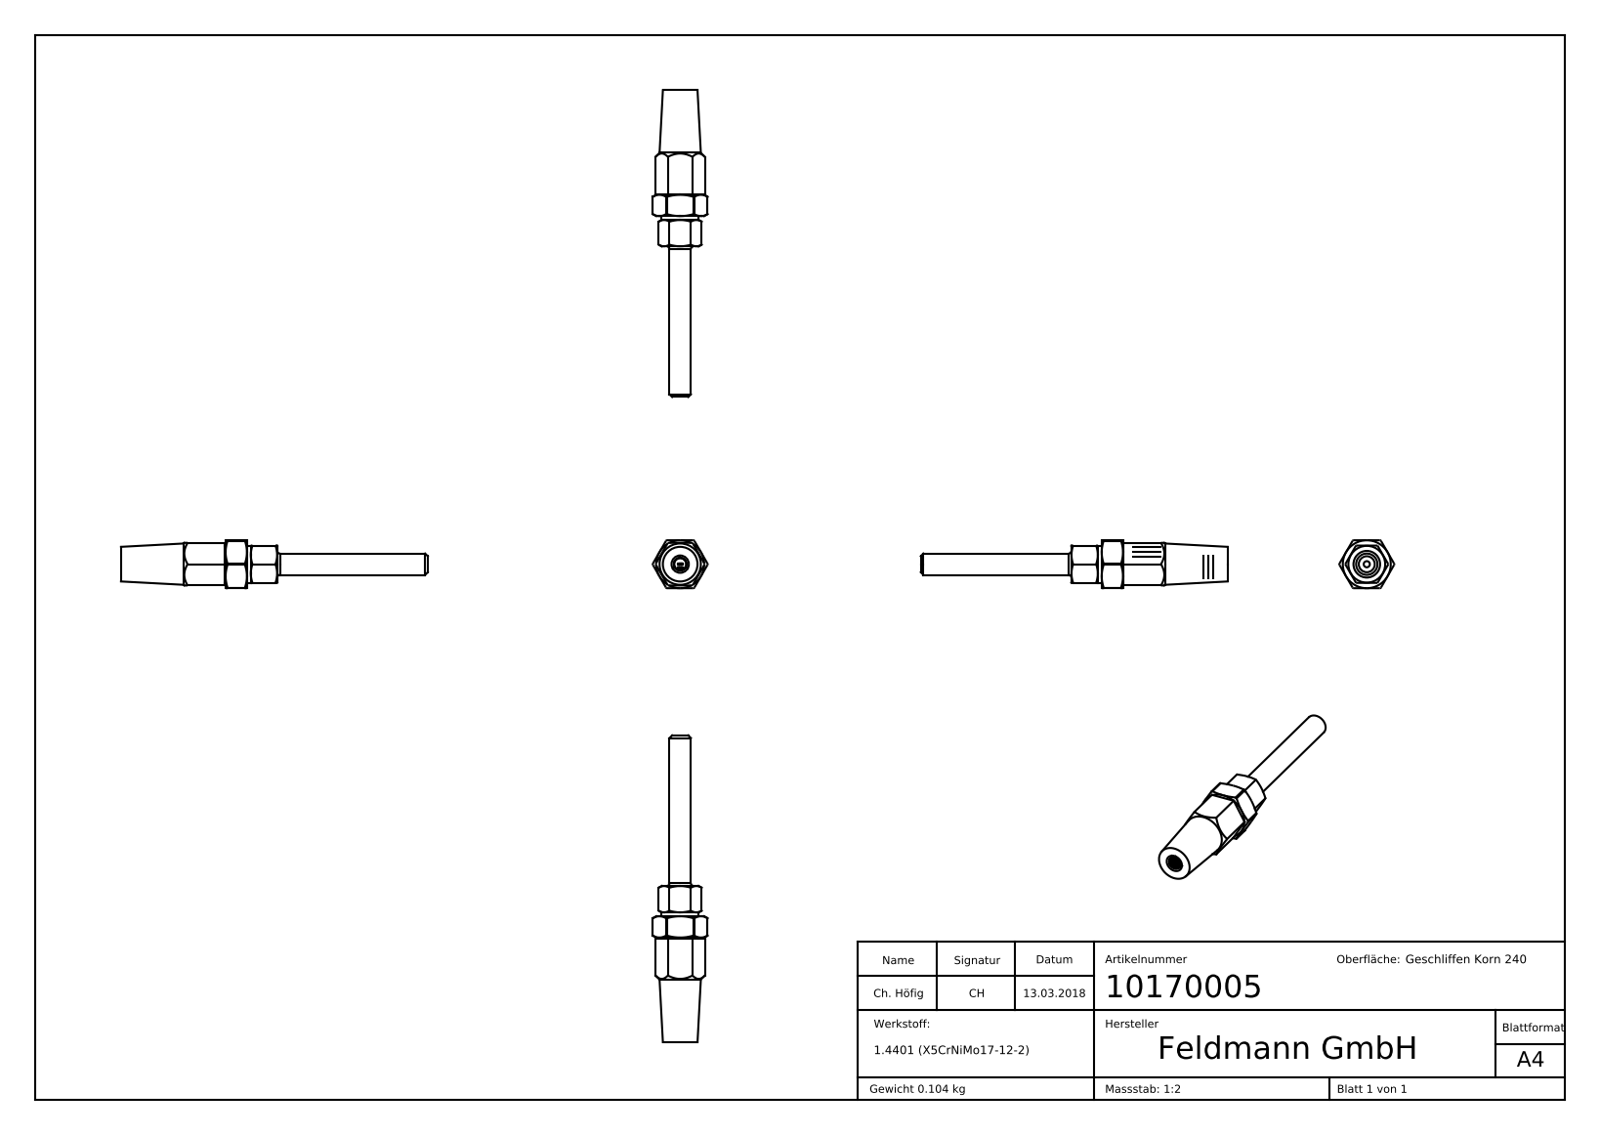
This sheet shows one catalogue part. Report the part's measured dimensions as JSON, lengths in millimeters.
{"part_name": "1017000X Teil3_10170005 Teil3; 1017000X Teil5_10170005 Teil5; 1017000X Teil4_10170005 Teil4; 1017000X Teil1_10170005 Teil1 (+3 more)", "step_written_by": "SolidWorks 2015 (CONFIG_CONTROL_DESIGN)", "units": "millimeters", "bodies": {"solids": 8, "faces": 549, "planar": 144, "cylindrical": 132, "other": 273}, "overall_size": [115.15, 20.63, 18], "volume_mm3": 13086, "surface_area_mm2": 8994, "round_holes": [[12, 2], [2.3, 1], [4.5, 1], [6, 1], [6.5, 1], [8.2, 1]], "round_bosses_or_shafts": [[14, 1], [10, 1], [8, 1]], "partial_cylinders_radius": [[0.5, 6]], "face_to_face_distances": [16, 2, 0.99, 1.01, 14, 18, 15.01, 14.99, 0.97, 1.03]}
